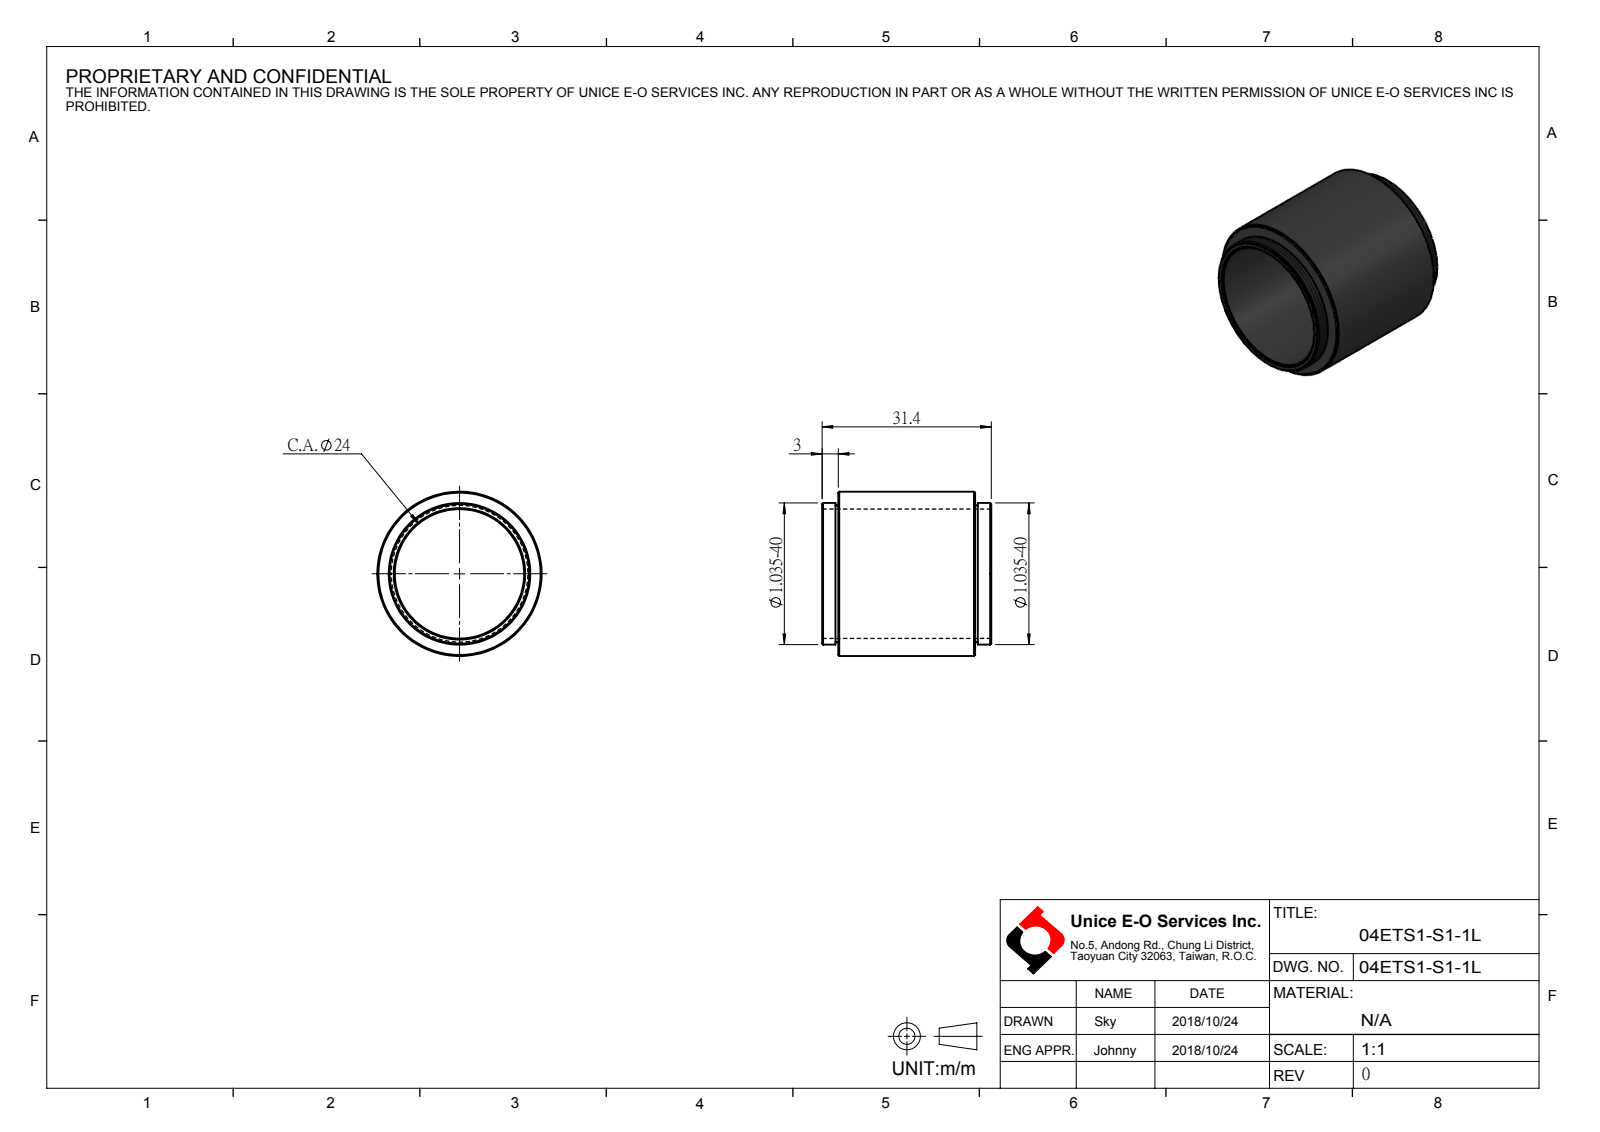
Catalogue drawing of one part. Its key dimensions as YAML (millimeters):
part_name: "04ETS1-S1-1L"
step_written_by: "SolidWorks 2016 (AUTOMOTIVE_DESIGN)"
units: millimeters
bodies: {solids: 0, faces: 28, planar: 4, cylindrical: 12, other: 12}
overall_size: [31.4, 30.5, 30.5]
round_holes:
  - {diameter: 24, count: 1}
round_bosses_or_shafts:
  - {diameter: 30.5, count: 1}
  - {diameter: 26.29, count: 1}
  - {diameter: 25.37, count: 1}
face_to_face_distances: [25.4, 3, 28.4, 31.4]
